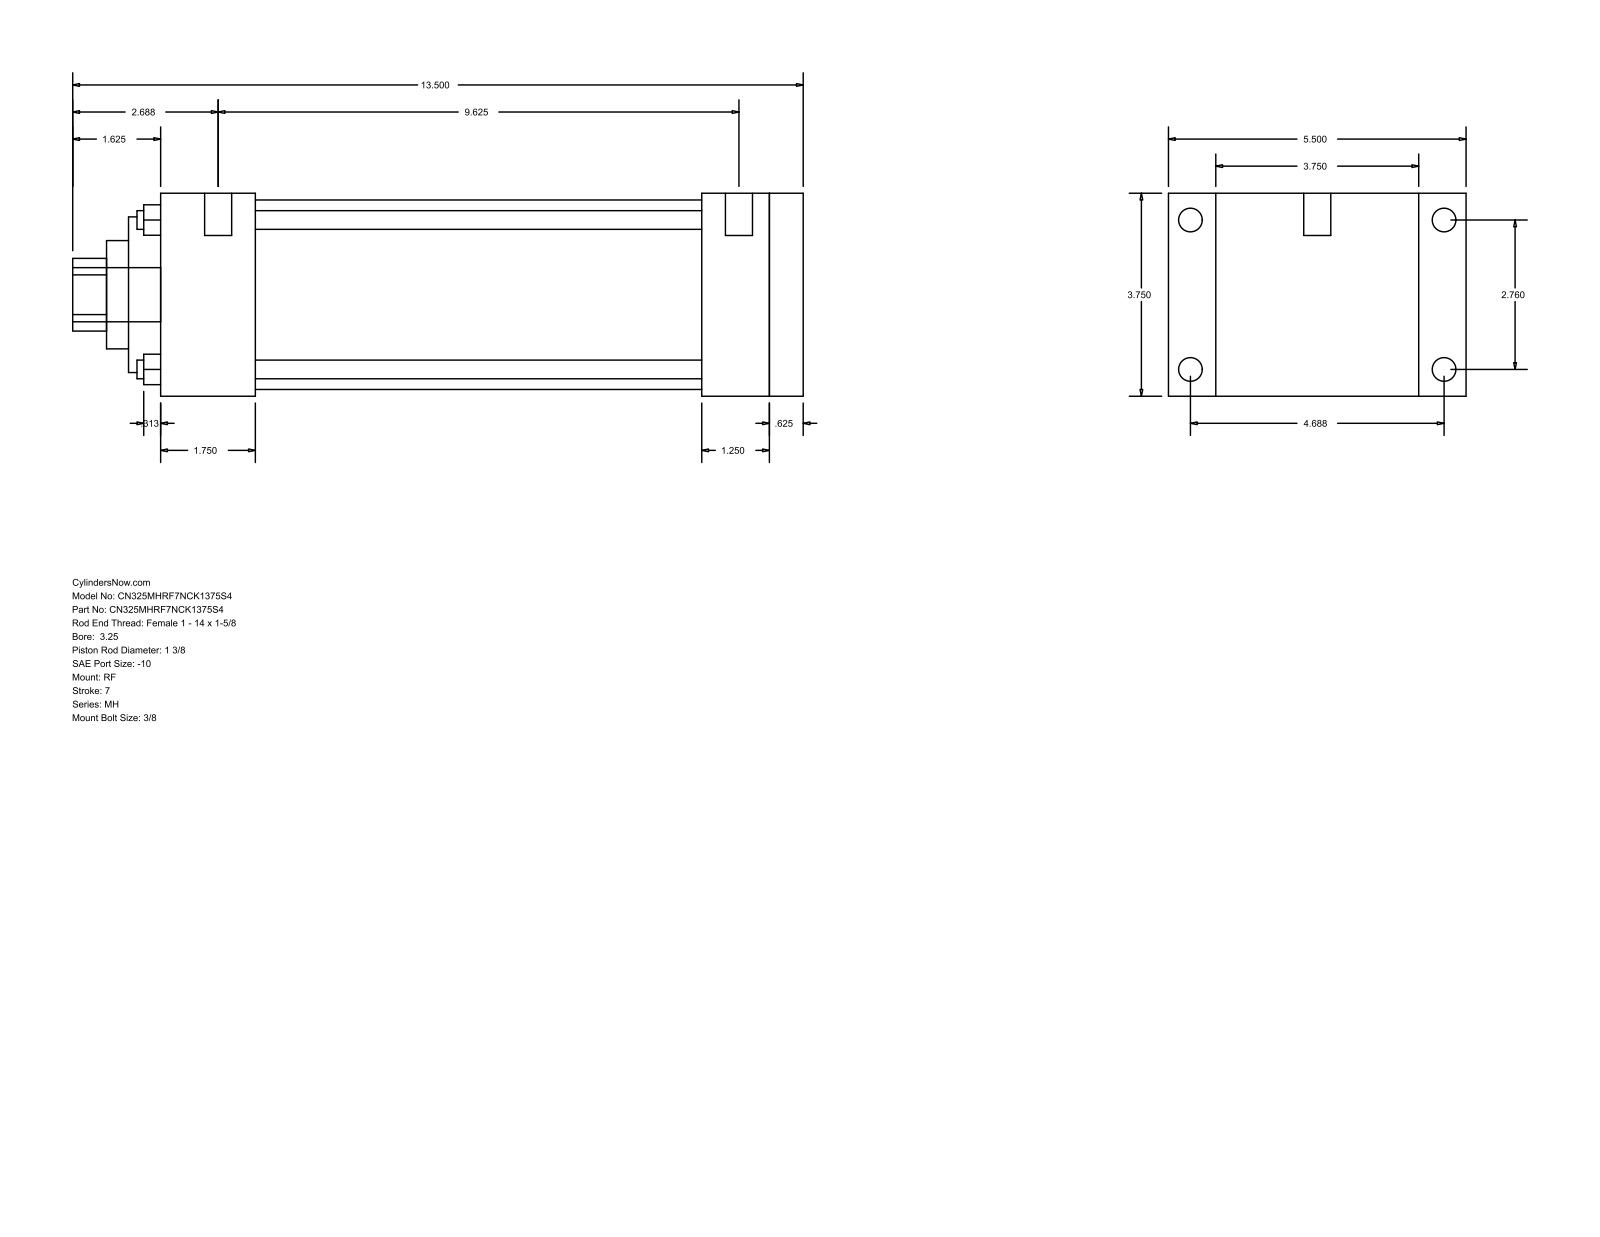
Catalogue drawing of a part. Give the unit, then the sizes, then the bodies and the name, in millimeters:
Units: millimetres
Overall size (bounding box): 342.9 × 139.7 × 95.25
Round holes (diameter × count): ⌀8.76 ×4, ⌀34.92 ×1, ⌀50.8 ×1, ⌀73.03 ×1, ⌀88.9 ×1
Round bosses / shafts (diameter × count): ⌀11.13 ×4, ⌀5.56 ×4, ⌀12.7 ×2, ⌀25.4 ×1
Partial cylindrical surfaces — rounded edges, fillets, slot ends (radius × count): R17.06 ×1
Main face-to-face distances: 95.24, 301.63, 15.88, 285.75, 22.23, 117.47, 44.45, 241.3, 257.18, 254
Hole centre spacings: 49.57, 70.1, 99.14
Bodies: 0 solids, 94 faces (65 planar, 29 cylindrical, 0 other)
Part name (STEP PRODUCT): MH_RF__0325_1.375
STEP written by: GSSL Pune (CONFIG_CONTROL_DESIGN)
